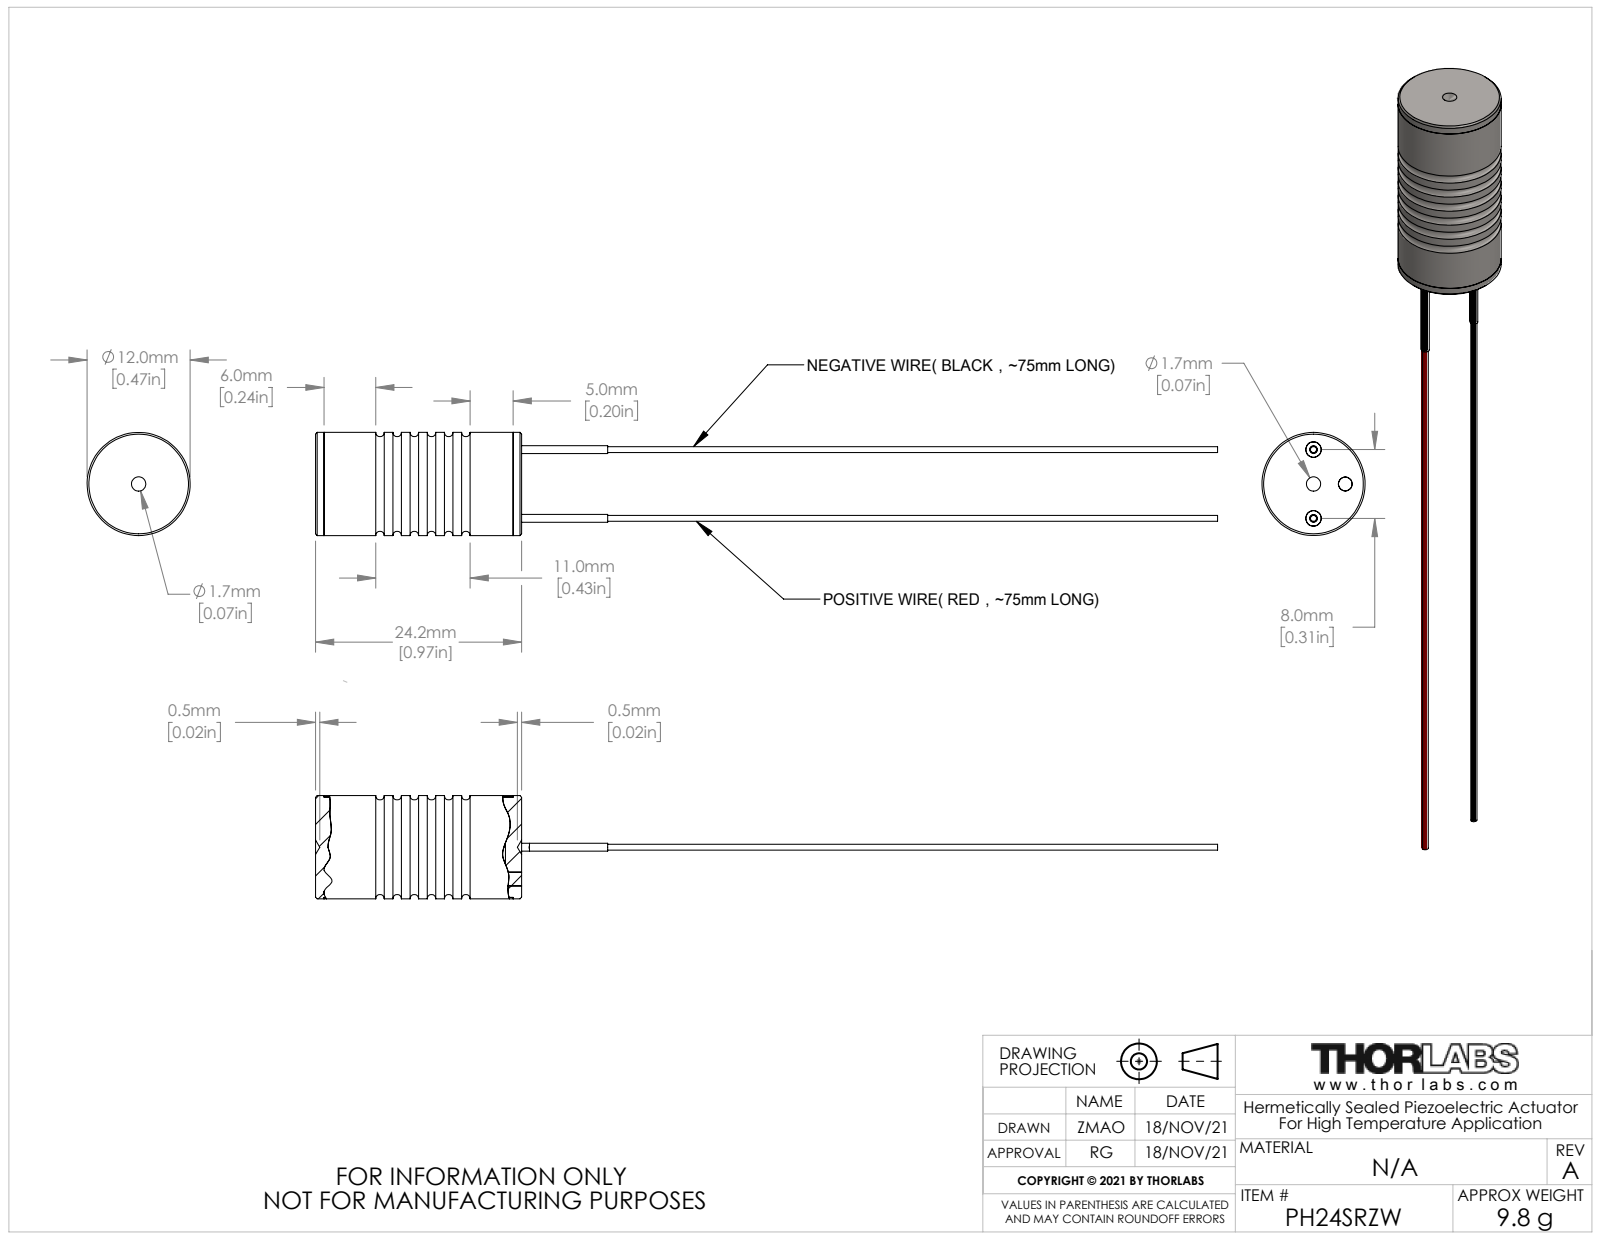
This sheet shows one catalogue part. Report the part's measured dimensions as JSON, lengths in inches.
{"part_name": "CTN017873-E0W", "step_written_by": "SolidWorks 2018 (CONFIG_CONTROL_DESIGN)", "units": "inches", "bodies": {"solids": 12, "faces": 181, "planar": 33, "cylindrical": 78, "other": 70}, "overall_size": [4.134, 0.472, 0.472], "volume_in3": 0.05, "surface_area_in2": 5.034, "round_holes": [[0.031, 2], [0.071, 2], [0.063, 1], [0.315, 1], [0.394, 1], [0.461, 1]], "round_bosses_or_shafts": [[0.035, 2], [0.028, 2], [0.472, 1]], "partial_cylinders_radius": [[0.01, 4]], "face_to_face_distances": [0.079, 0.945, 0.787, 0.866, 0.157, 0.087, 0.701, 0.78, 0.858, 0.039], "hole_center_spacings": [0.157, 0.215, 0.146, 0.315]}
